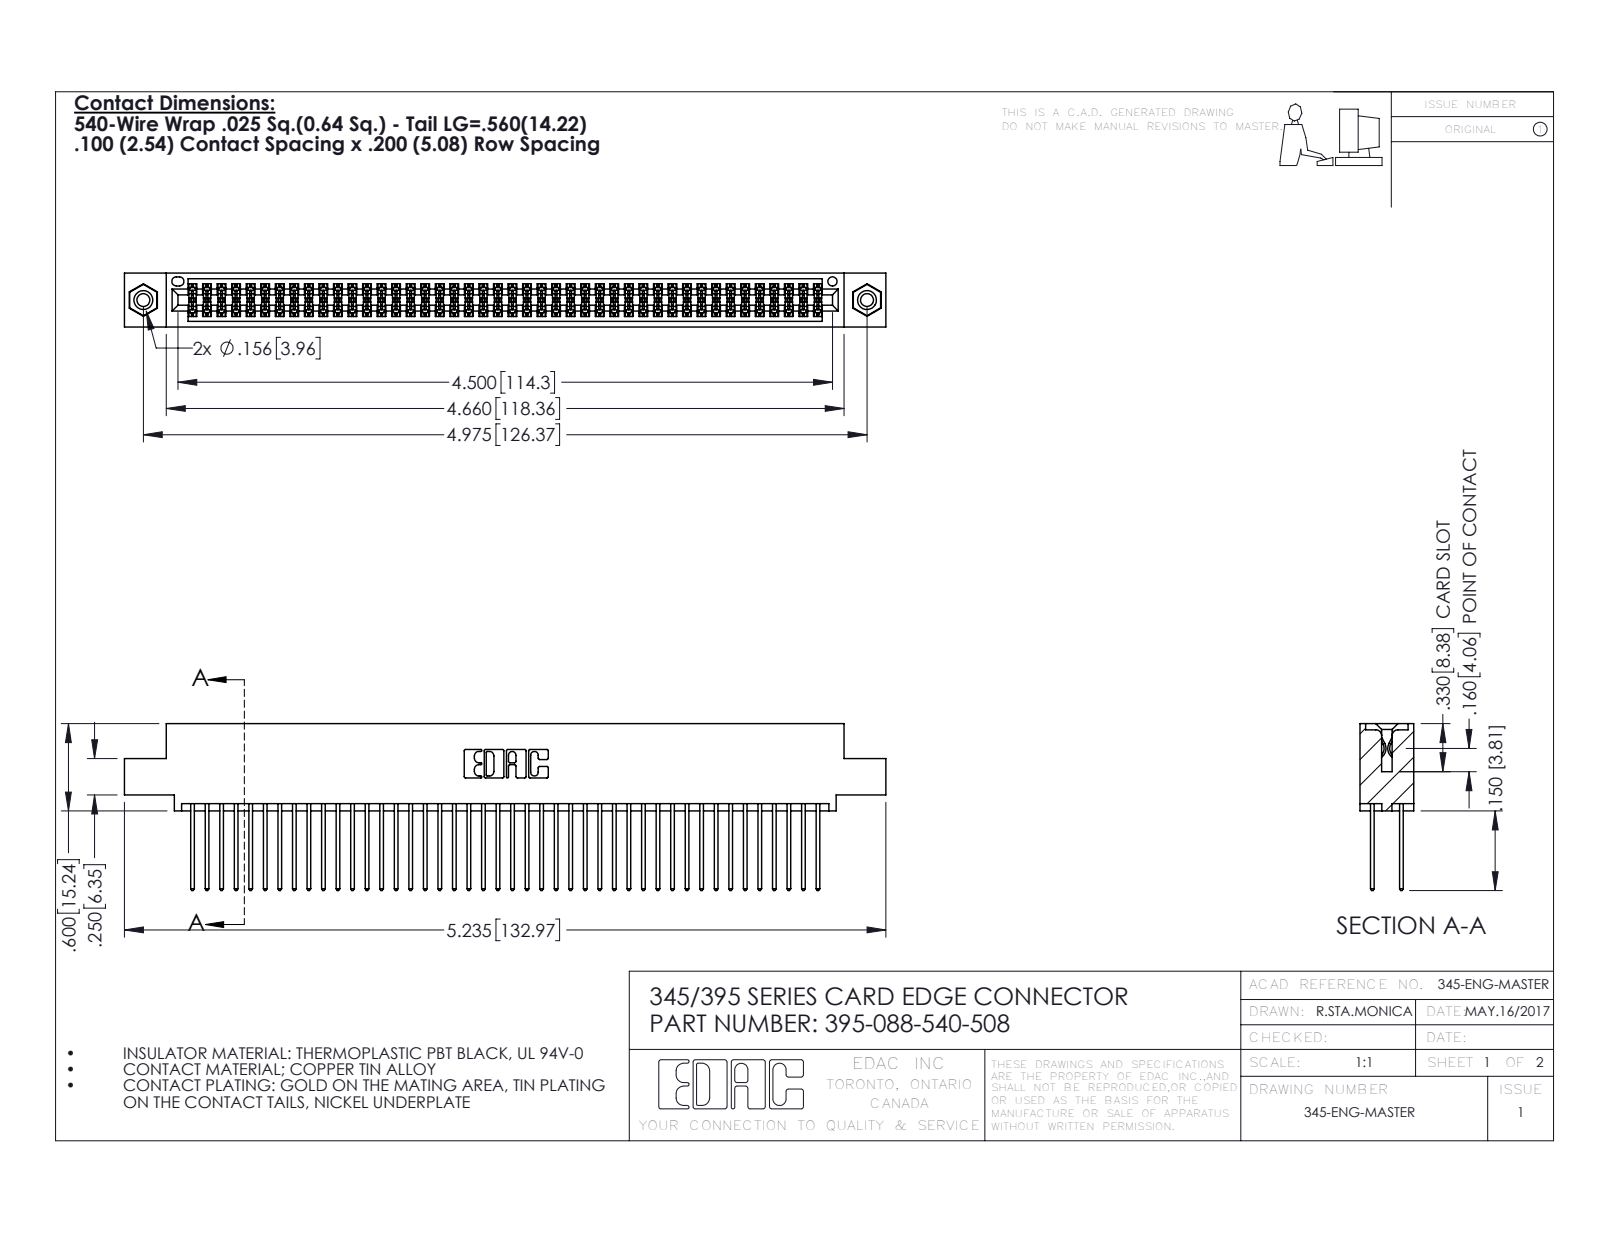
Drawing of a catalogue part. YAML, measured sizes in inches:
part_name: "345-292-001_345-293-140; 395-088-540-508; 345 Part_0.110 Offset - 0.156 Dia-TI; 345-250-001_345-250-003-102"
step_written_by: "SolidWorks 2016 (CONFIG_CONTROL_DESIGN)"
units: inches
bodies: {solids: 91, faces: 4590, planar: 3020, cylindrical: 1554, other: 16}
overall_size: [5.235, 1.147, 0.37]
volume: 0.805
surface_area: 32.84
round_holes:
  - {diameter: 0.089, count: 2}
  - {diameter: 0.125, count: 2}
  - {diameter: 0.156, count: 2}
  - {diameter: 0.064, count: 1}
round_bosses_or_shafts:
  - {diameter: 0.155, count: 2}
partial_cylinders:
  - {radius: 0.006, count: 132}
  - {radius: 0.01, count: 88}
  - {radius: 0.01, count: 22}
  - {radius: 0.007, count: 6}
  - {radius: 0.031, count: 6}
  - {radius: 0.026, count: 3}
  - {radius: 0.014, count: 2}
  - {radius: 0.019, count: 2}
face_to_face_distances: [0.072, 0.298, 0.2, 0.098, 0.272, 0.025, 0.37, 0.225, 0.175, 0.149]
hole_center_spacings: [0.27, 4.739, 4.975]
